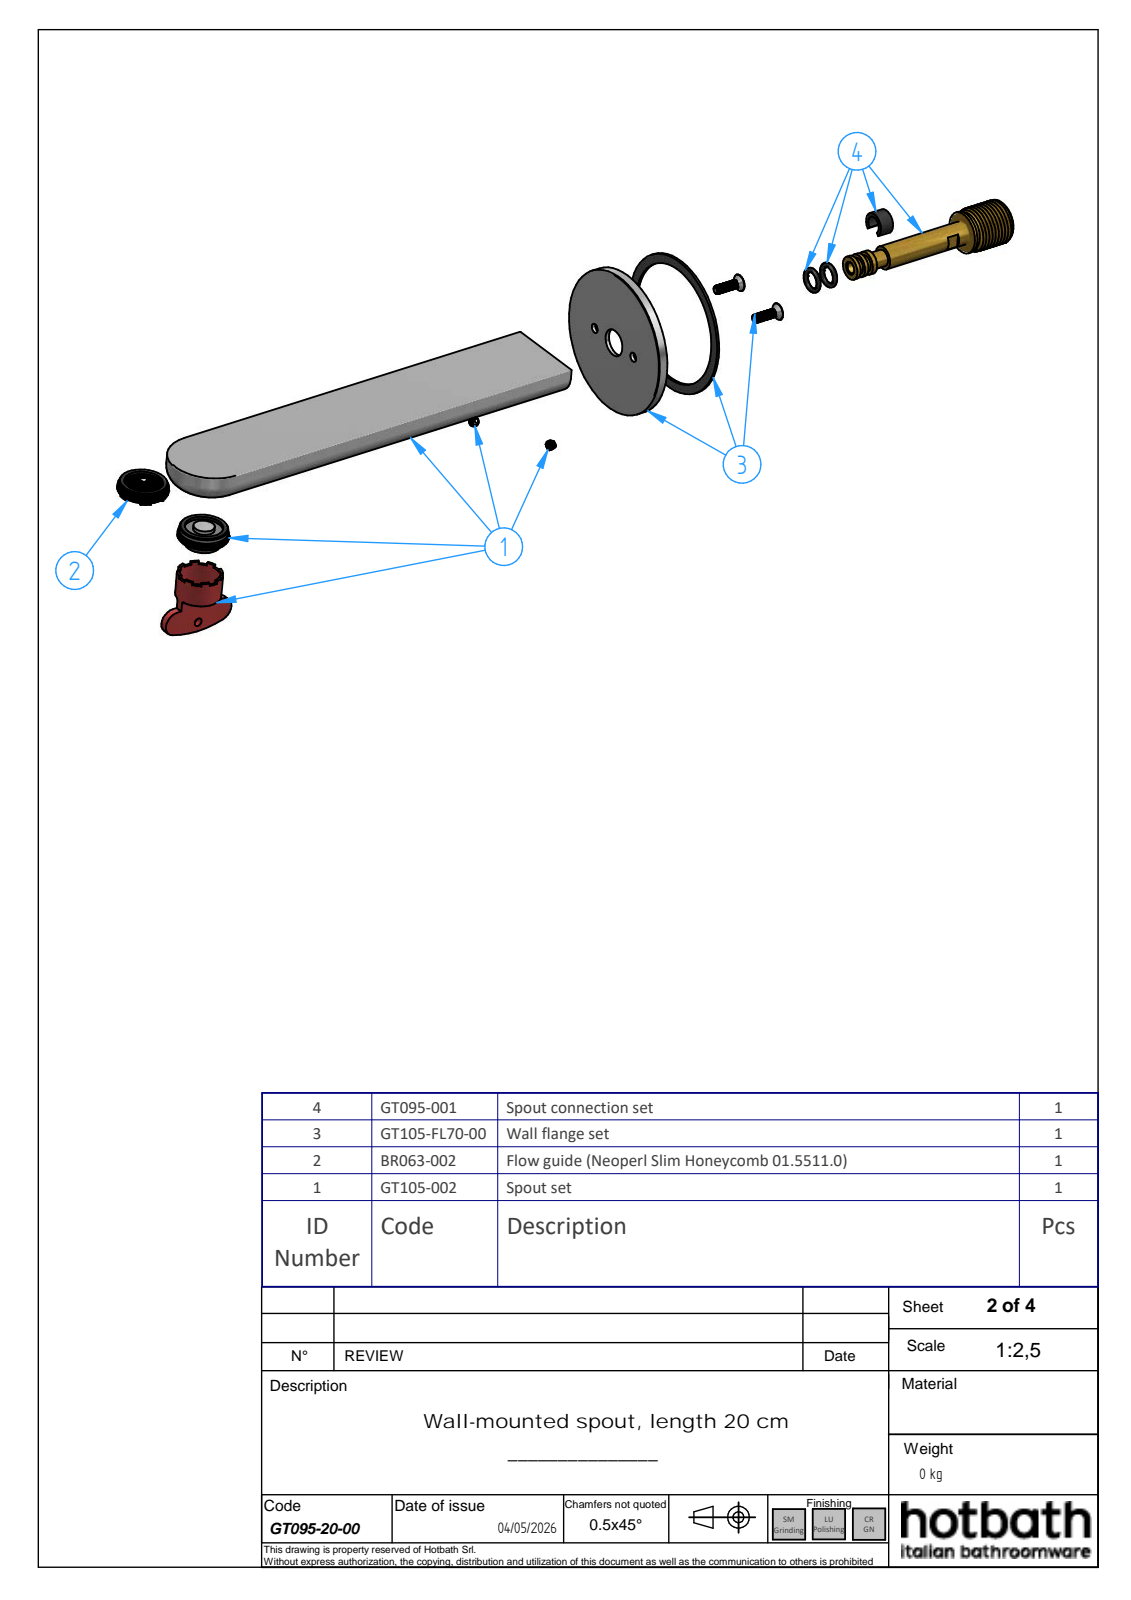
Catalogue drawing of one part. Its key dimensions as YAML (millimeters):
part_name: "GT095-20-00; GT105-002_oa_0; CB095-16; GT003-002_oa_1 (+5 more)"
step_written_by: "Solid Edge (AUTOMOTIVE_DESIGN)"
units: millimeters
bodies: {solids: 6, faces: 937, planar: 822, cylindrical: 67, other: 48}
overall_size: [220, 70, 70]
volume: 110953
surface_area: 42299
round_holes:
  - {diameter: 3.24, count: 4}
  - {diameter: 4.5, count: 4}
  - {diameter: 7, count: 1}
  - {diameter: 11.5, count: 1}
  - {diameter: 12.5, count: 1}
  - {diameter: 13, count: 1}
  - {diameter: 15.8, count: 1}
  - {diameter: 16, count: 1}
  - {diameter: 18, count: 1}
  - {diameter: 21, count: 1}
  - {diameter: 21.8, count: 1}
  - {diameter: 22.92, count: 1}
round_bosses_or_shafts:
  - {diameter: 4, count: 2}
  - {diameter: 3.24, count: 2}
  - {diameter: 70, count: 1}
  - {diameter: 26, count: 1}
  - {diameter: 22.7, count: 1}
  - {diameter: 20, count: 1}
  - {diameter: 18.4, count: 1}
partial_cylinders:
  - {radius: 0.3, count: 5}
  - {radius: 9, count: 2}
  - {radius: 9.5, count: 1}
  - {radius: 10.5, count: 1}
  - {radius: 20, count: 1}
  - {radius: 70, count: 1}
face_to_face_distances: [4.5, 0.5, 4, 40, 6.4, 2, 1.5, 1.38, 2.88, 9.28]
hole_center_spacings: [15, 30]
